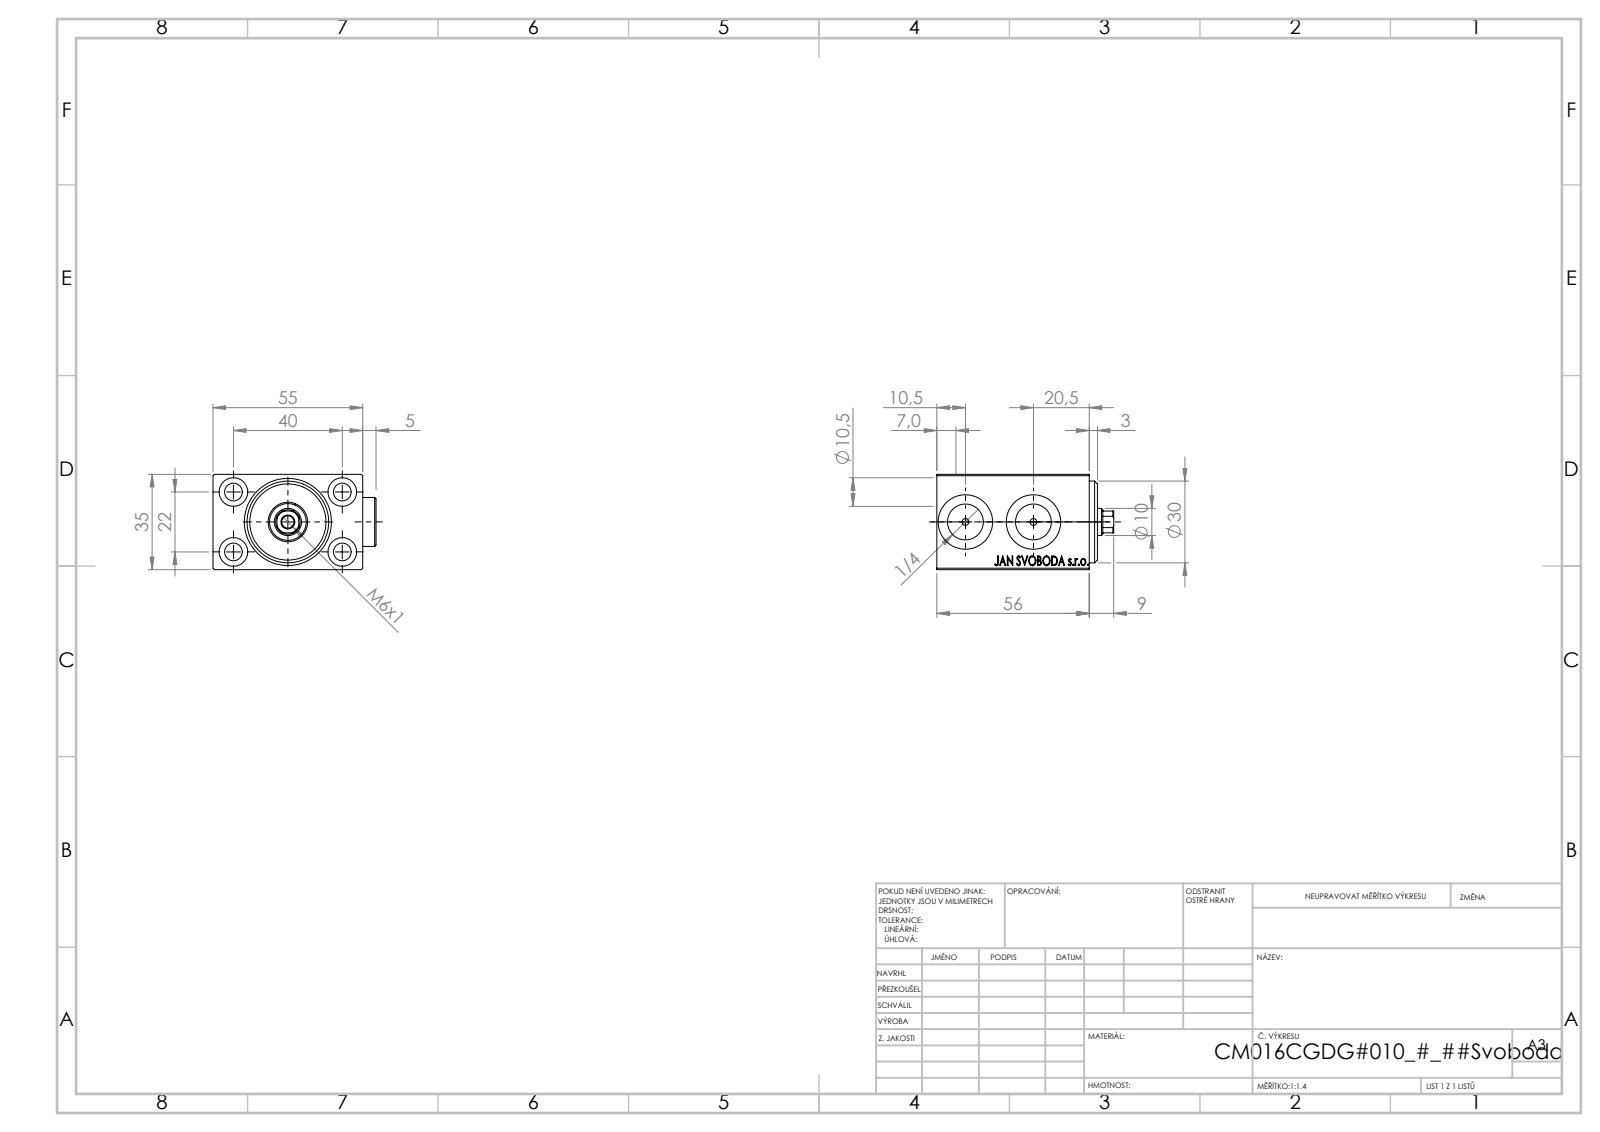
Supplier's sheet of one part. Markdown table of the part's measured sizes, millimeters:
| quantity | value |
| --- | --- |
| part name | Zatka_OIL_PORT; V450CM_C_VCP; V450CM_C_Body; V450CM_VC_B |
| STEP written by | SolidWorks 2019 (CONFIG_CONTROL_DESIGN) |
| units | millimeters |
| bodies | 5 solids, 919 faces (443 planar, 78 cylindrical, 398 other) |
| overall size | 65 × 59.9 × 35 |
| volume | 93 219 mm³ |
| surface area | 31 381 mm² |
| round holes (diameter × count) | 6.5 × 4, 10.5 × 4, 2.5 × 2, 13.16 × 2, 20 × 2, 4.5 × 1, 10 × 1, 13.5 × 1, 14.5 × 1, 16 × 1, 18 × 1, 30 × 1 |
| round bosses / shafts (diameter × count) | 18 × 2 |
| partial cylindrical surfaces (radius × count) | 4.5 × 1 |
| main face-to-face distances | 35, 5, 51, 55, 54.9, 56, 2, 42, 3, 8 |
| hole center spacings | 22.83, 22, 40, 45.65, 25 |
